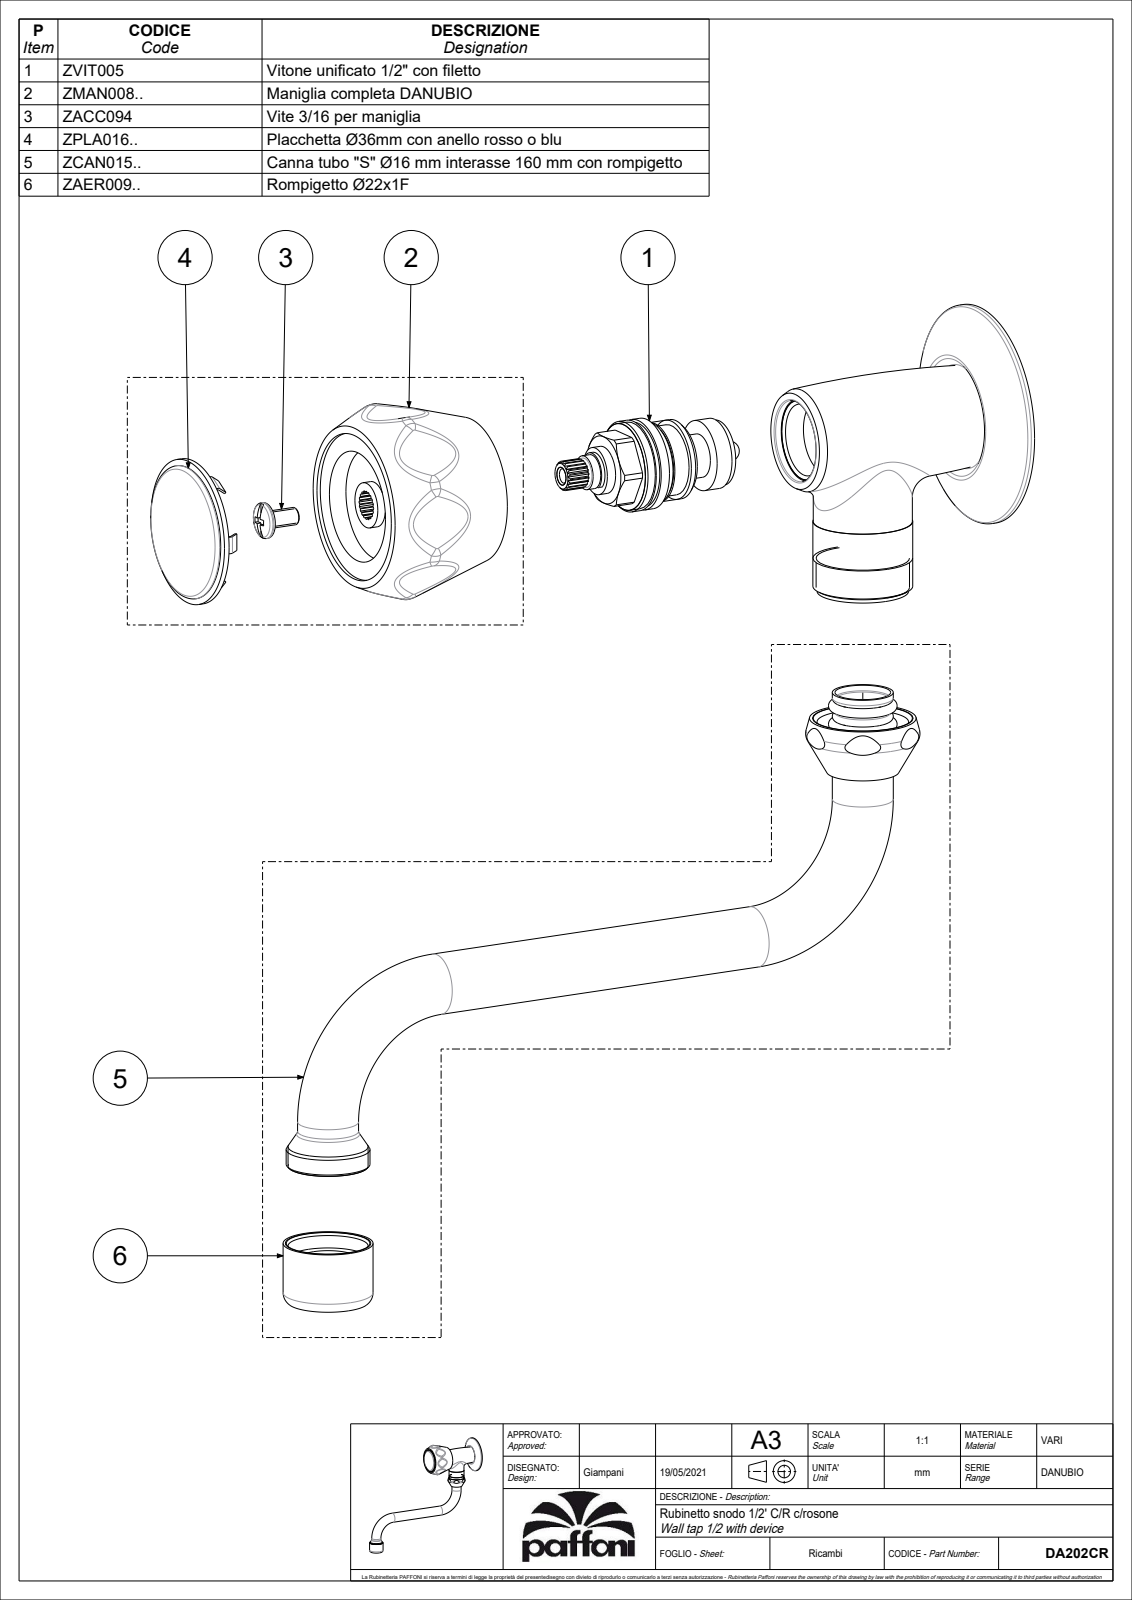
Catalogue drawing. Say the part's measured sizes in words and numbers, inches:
The part is named "DA202CR". Its 3-D file was written by "CREO PARAMETRIC BY PTC INC, 2020044 (CONFIG_CONTROL_DESIGN)". It is 1 solid with 136 faces: 16 planar, 28 cylindrical and 92 other. Overall it measures 8.496 by 7.043 by 2.283 inches. Its volume is 10.94 cubic inches and its surface area 51.49 square inches. Round bosses or shafts: 3 of diameter 0.63, 1 of diameter 2.283, 1 of diameter 1.516, 1 of diameter 1.031, 1 of diameter 1.024, 1 of diameter 0.929, 1 of diameter 0.866, 1 of diameter 0.827. Partial cylindrical surfaces (rounded edges, fillets, slot ends): 8 of radius 0.839. The main face-to-face distances are 2.13, 3.52, 1.39, 0.264, 2.394, 3.783, 3.799, 3.535, 1.406, 0.016.
